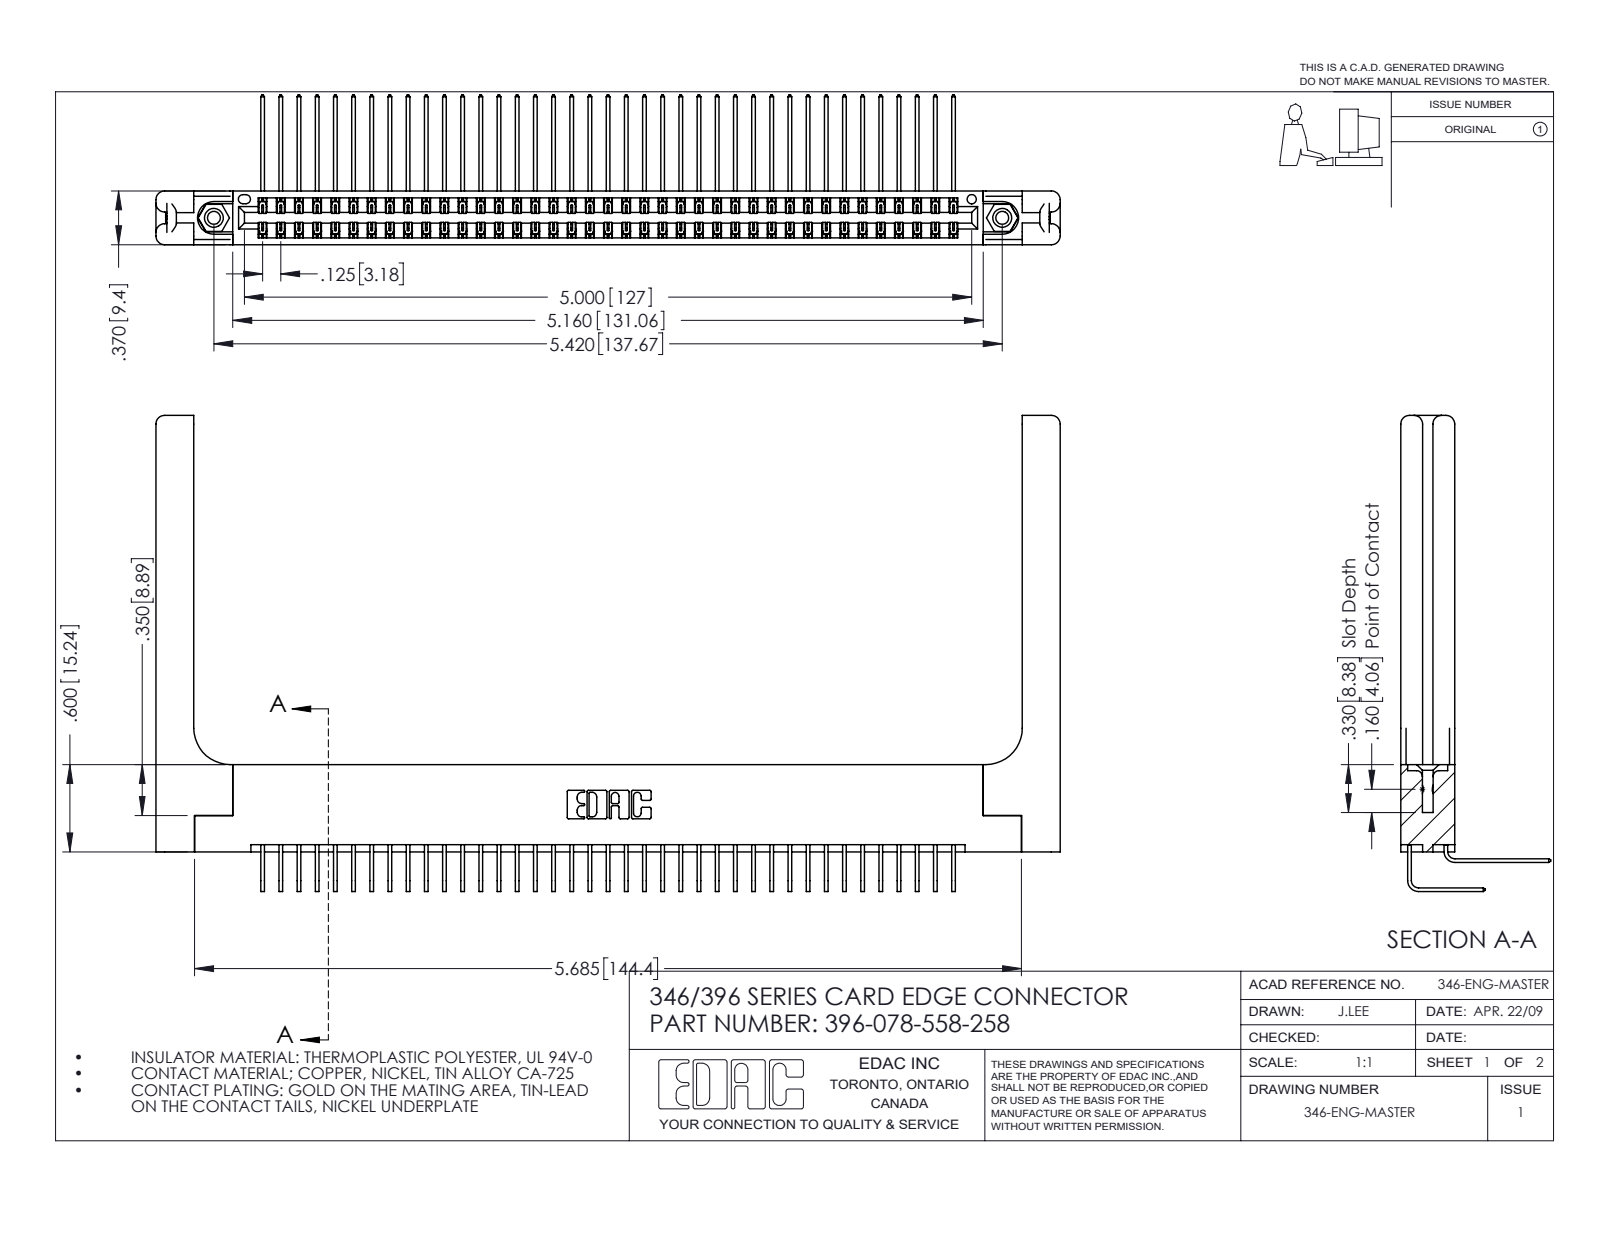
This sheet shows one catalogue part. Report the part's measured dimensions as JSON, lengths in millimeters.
{"part_name": "396-078-558-258; 345-250-001_345-250-001-102; 346-220-058_345-220-058; 346 Part_Flush Mounting Lugs - 0.156 Dia-TH (+2 more)", "step_written_by": "SolidWorks 2016 (CONFIG_CONTROL_DESIGN)", "units": "millimeters", "bodies": {"solids": 83, "faces": 4590, "planar": 3110, "cylindrical": 1420, "other": 60}, "overall_size": [157.9, 83.1, 26.2], "volume_mm3": 23320, "surface_area_mm2": 28830, "round_holes": [[2.3, 2], [3.2, 2], [4, 2], [1.6, 1]], "round_bosses_or_shafts": [[3.9, 2]], "partial_cylinders_radius": [[0.2, 117], [0.3, 22], [1.5, 16], [0.2, 6], [0.8, 6], [0.7, 3], [0.4, 2], [0.6, 2]], "face_to_face_distances": [8.2, 1.2, 9.4, 1.8, 0.6, 7.6, 3.8, 3.8, 6.4, 7], "hole_center_spacings": [6.2, 132.4, 137.7]}
